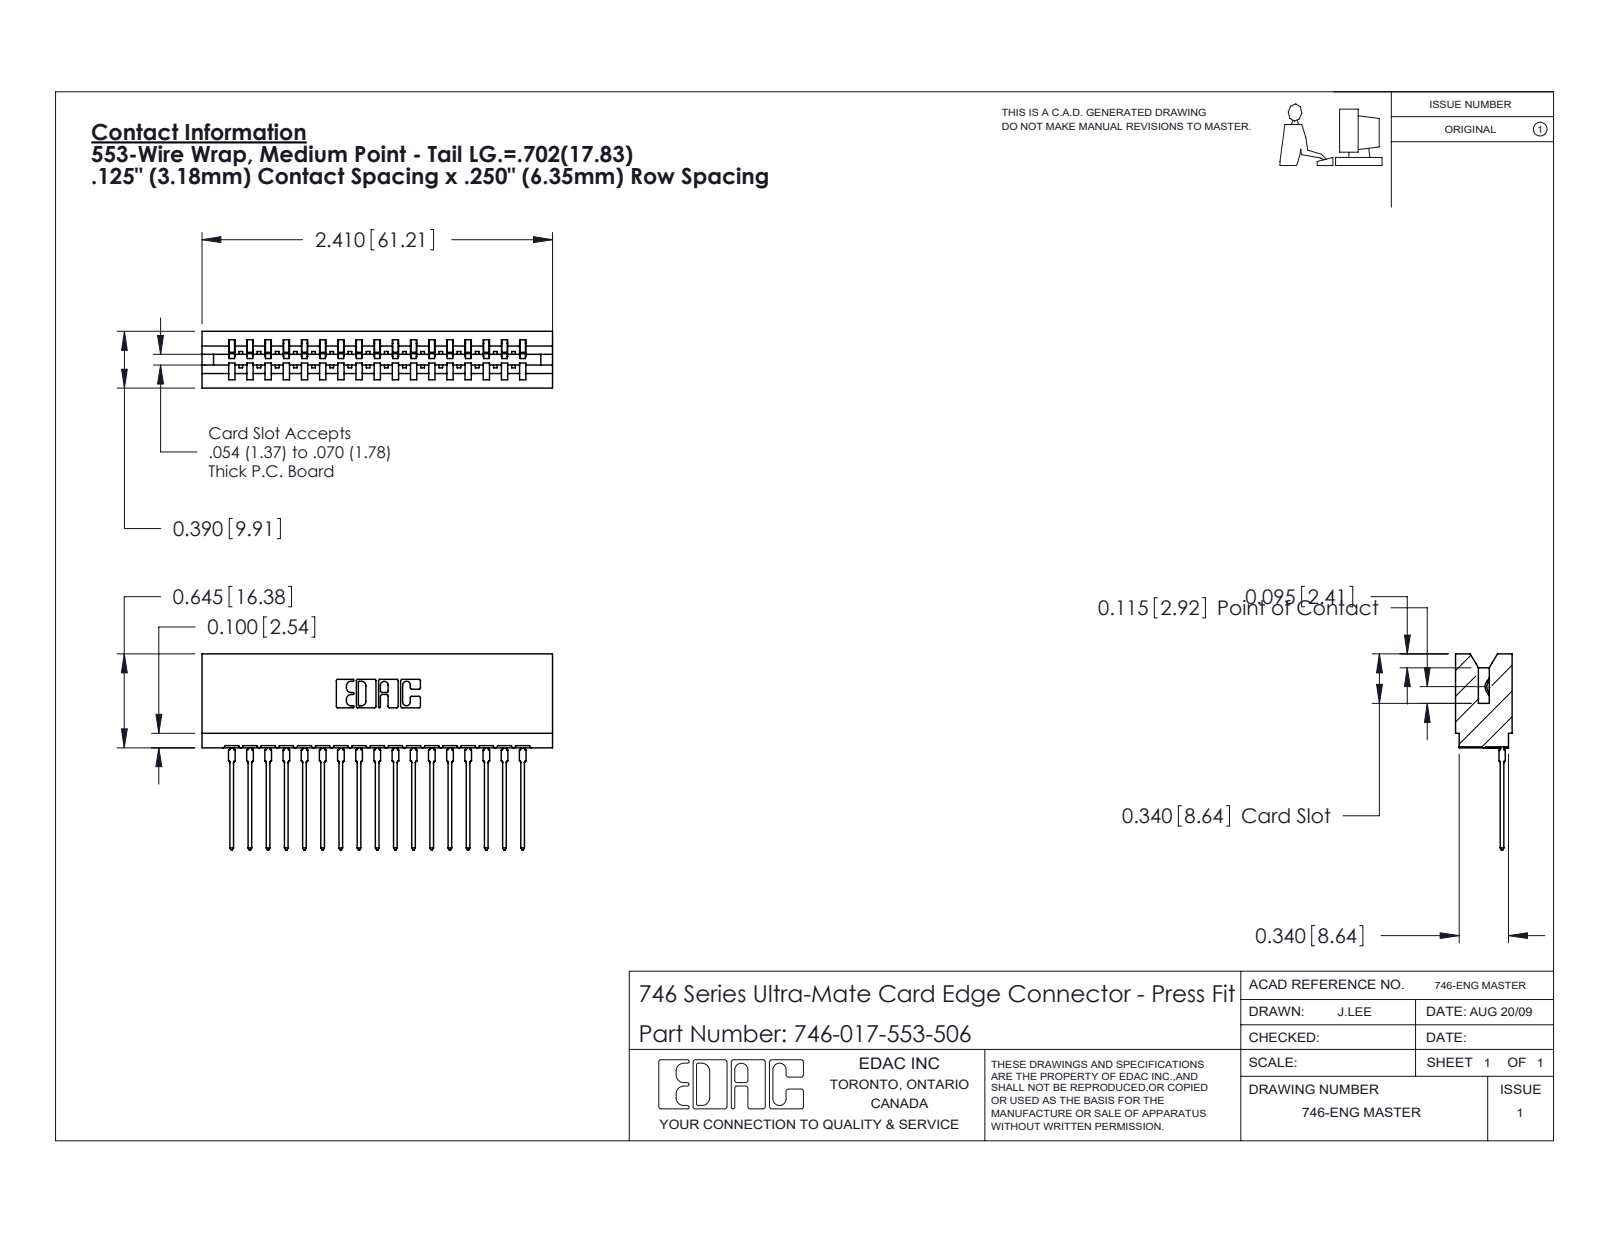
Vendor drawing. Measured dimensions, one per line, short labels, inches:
name: 746-017-553-506; 746-292-001_553; 746 Part_.340 Slot Depth - 06
written by: SolidWorks 2020 (CONFIG_CONTROL_DESIGN)
unit: in
bodies: 18 solids, 1934 faces (1127 planar, 365 cylindrical, 442 other)
size: 2.41 × 1.346 × 0.39
volume: 0.431 in³; area: 14.7 in²
rounds: 34× R0.021, 22× R0.01, 18× R0.015, 6× R0.007, 6× R0.031, 4× R0.005, 4× R0.011, 3× R0.026
face distances: 0.25, 0.057, 0.333, 0.39, 0.5, 0.125, 0.025, 0.307, 0.083, 0.042
